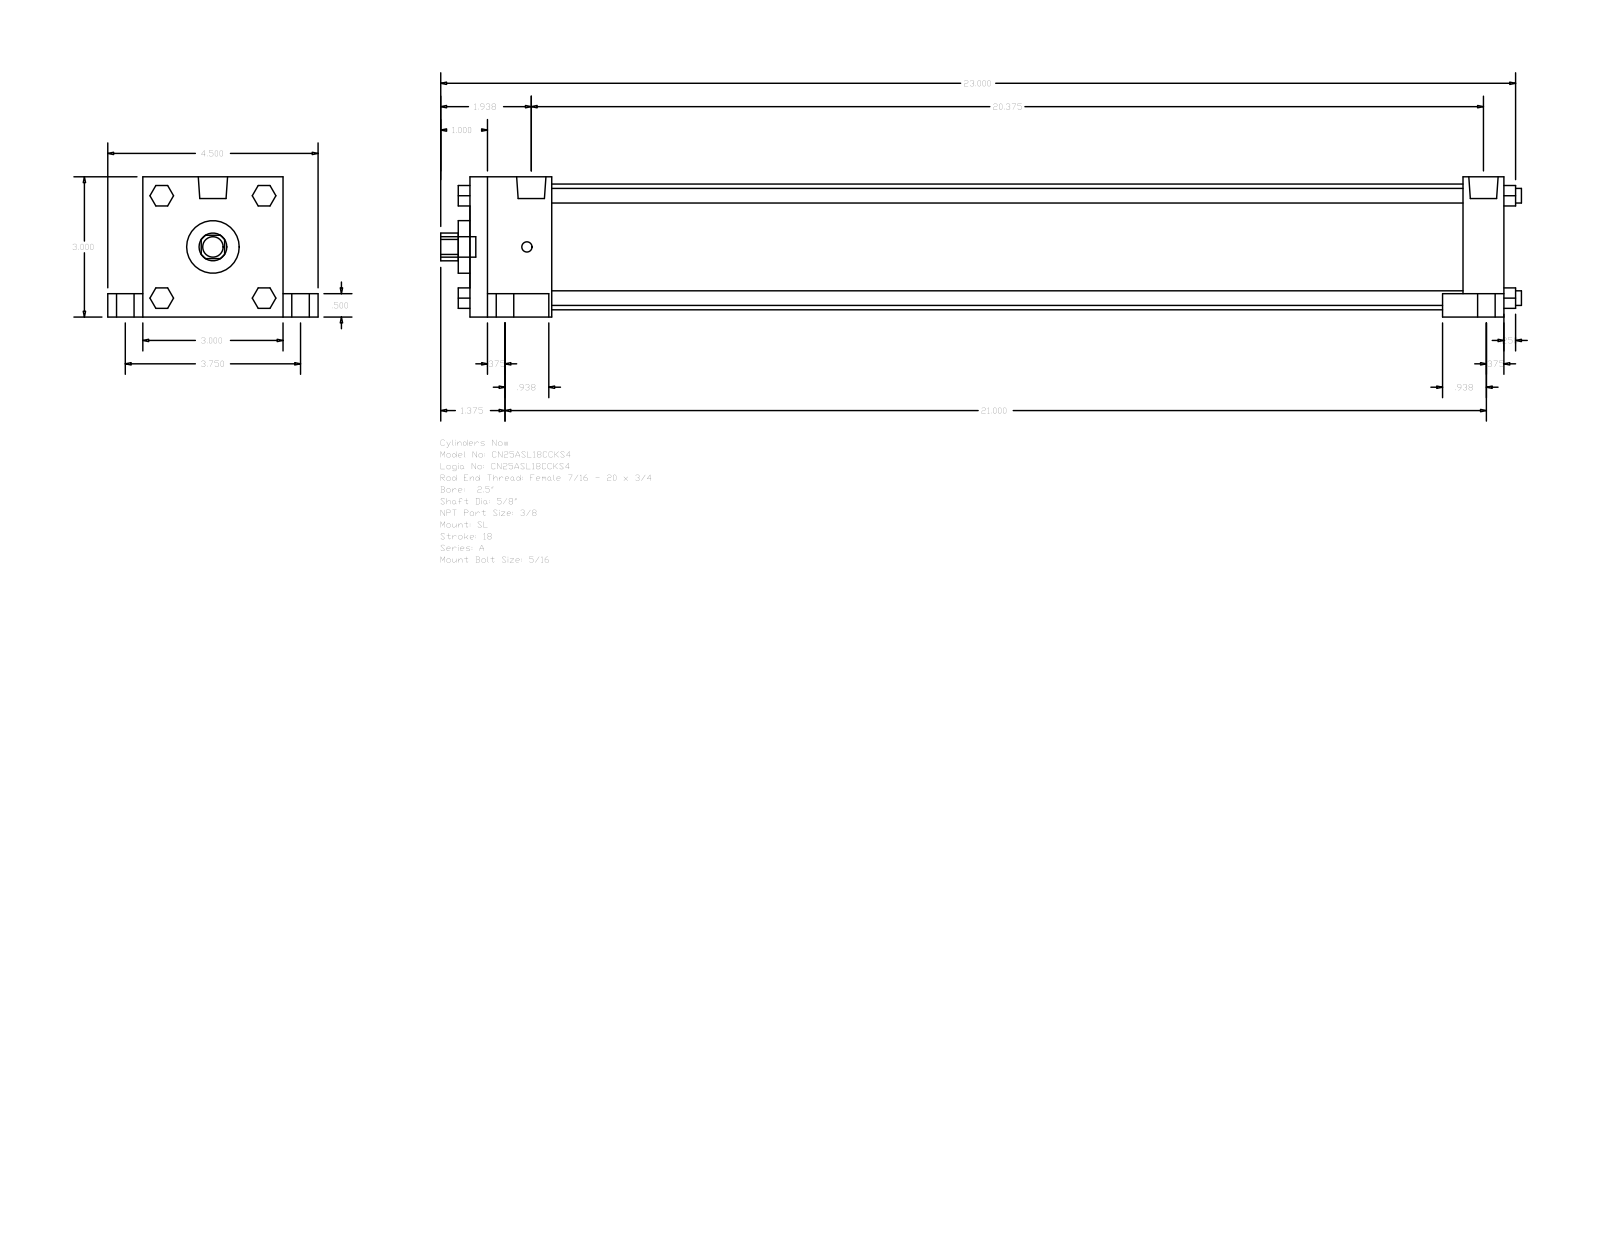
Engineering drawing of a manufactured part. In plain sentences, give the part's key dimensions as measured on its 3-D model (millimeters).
The part is named "A_SL__0250_0.625". Its 3-D file was written by "GSSL Pune (CONFIG_CONTROL_DESIGN)". It is 0 solids with 148 faces: 112 planar, 36 cylindrical and 0 other. Overall it measures 587.38 by 114.3 by 76.2 millimeters. Round holes: 1 of diameter 15.88, 1 of diameter 28.57, 1 of diameter 68.33. Round bosses or shafts: 4 of diameter 15.88, 4 of diameter 9.53, 4 of diameter 7.94, 4 of diameter 5.56, 2 of diameter 15.93, 1 of diameter 11.11. Partial cylindrical surfaces (rounded edges, fillets, slot ends): 1 of radius 7.54. The main face-to-face distances are 76.2, 561.97, 44.45, 517.52, 539.74, 495.29, 22.23, 12.7, 63.5, 19.05.
